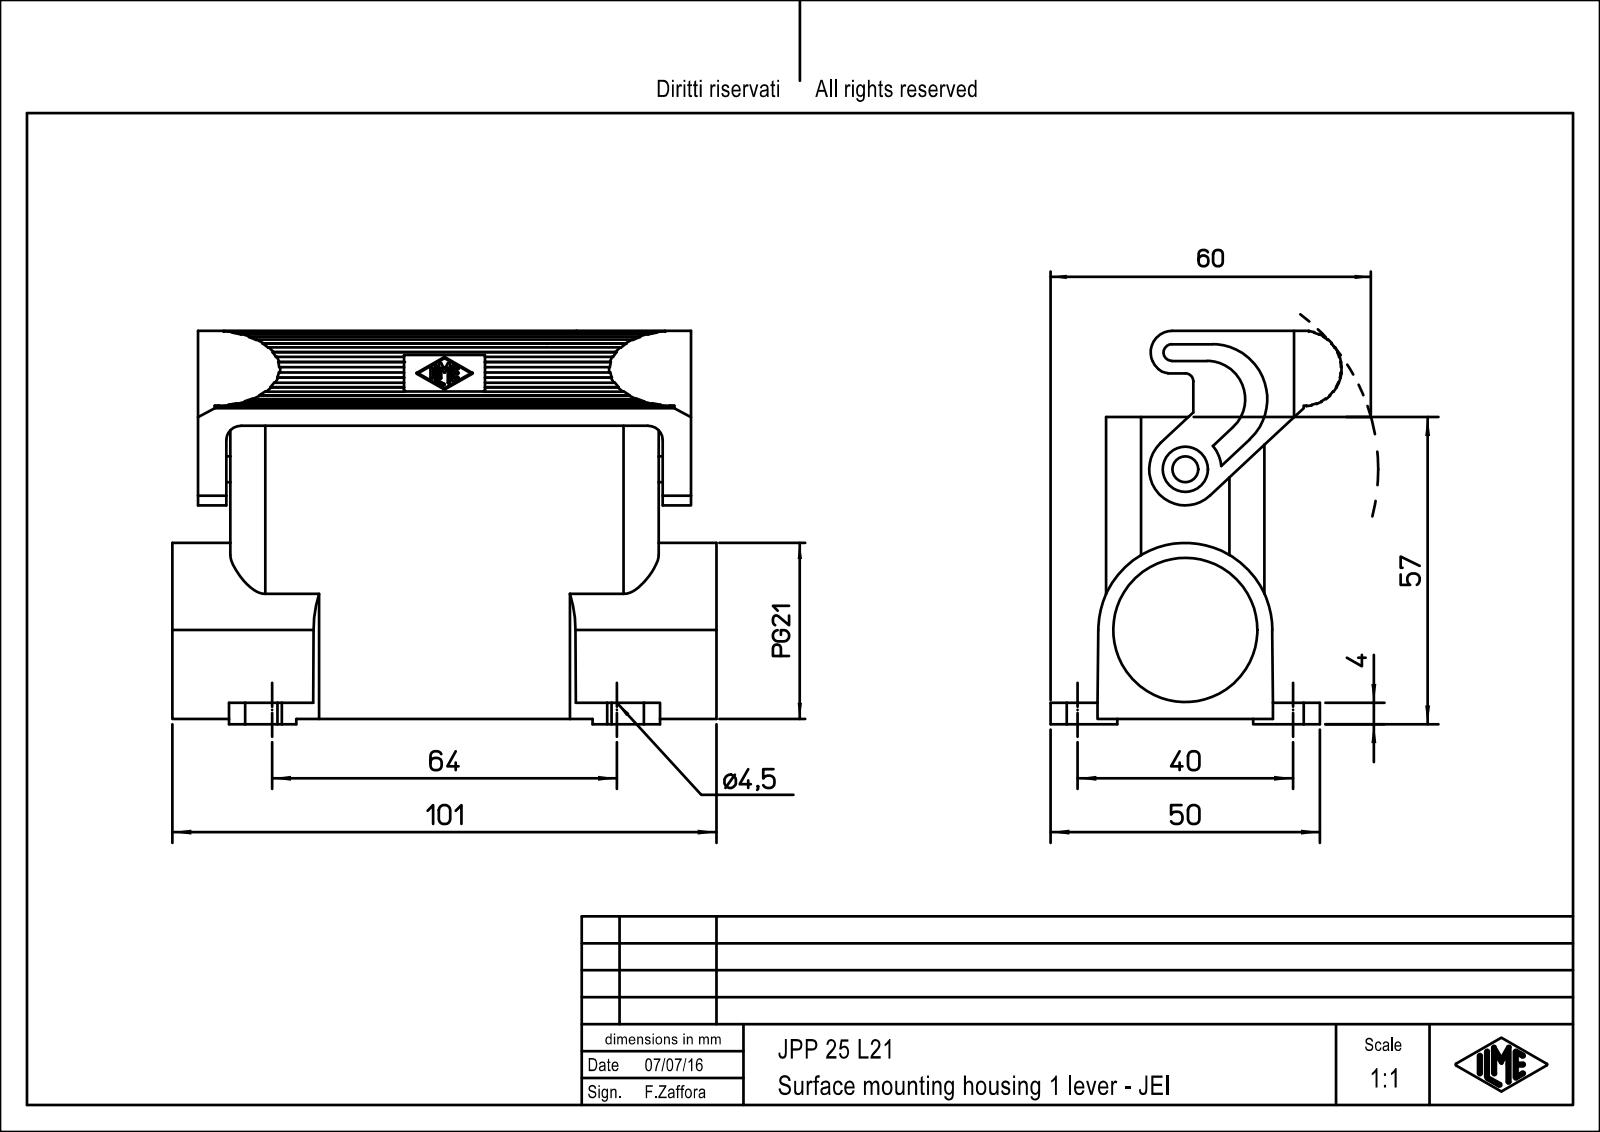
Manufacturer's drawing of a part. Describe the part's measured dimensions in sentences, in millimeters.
The part is named "JPP_25_L21". Its 3-D file was written by "PTC Creo Elements/Direct Modeling 19.0B 21-Mar-2015 (C) Parametric Technology GmbH (AUTOMOTIVE_DESIGN)". It is 1 solid with 309 faces: 170 planar, 139 cylindrical and 0 other. Overall it measures 101 by 73.01 by 54 millimeters. Its volume is 66 814 cubic millimeters and its surface area 40 550 square millimeters. Round holes: 4 of diameter 3, 4 of diameter 4.5, 1 of diameter 8.4, 1 of diameter 26.75. Round bosses or shafts: 1 of diameter 4.8. Partial cylindrical surfaces (rounded edges, fillets, slot ends): 15 of radius 0.2, 8 of radius 3.5, 5 of radius 3, 4 of radius 1, 4 of radius 6.5, 3 of radius 0.1, 2 of radius 0.3, 2 of radius 2.8. The main face-to-face distances are 2.75, 2.76, 23.89, 26.65, 29.4, 26.64, 3, 3.8, 6.56, 30.45. The hole center spacings are 12.04, 28.02, 66.1, 70.77, 16, 40, 64, 66.
